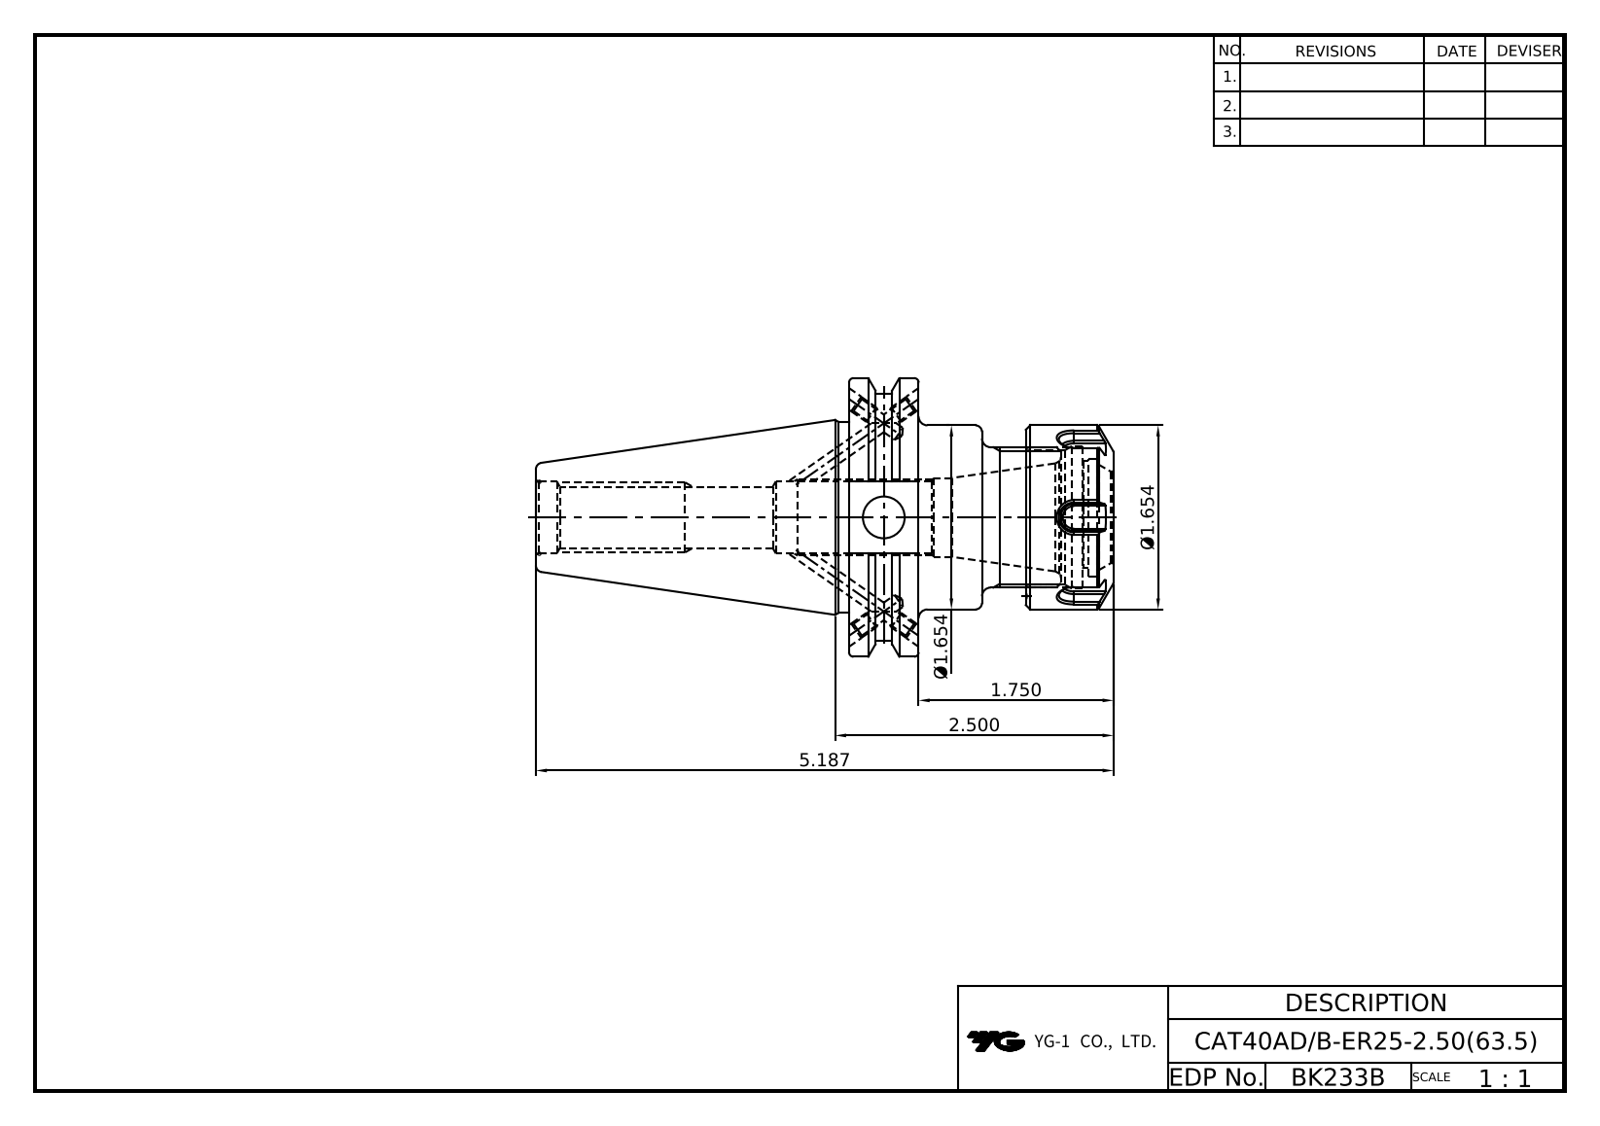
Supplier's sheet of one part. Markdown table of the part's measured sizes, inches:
| quantity | value |
| --- | --- |
| part name | LO-CAT40ADB-ER25-2.50; ER25NUT |
| STEP written by | Autodesk Inventor 2024 (AUTOMOTIVE_DESIGN) |
| units | inches |
| bodies | 2 solids, 164 faces (69 planar, 44 cylindrical, 51 other) |
| overall size | 5.187 × 2.5 × 2.405 |
| volume | 8.223 in³ |
| surface area | 51.17 in² |
| round holes (diameter × count) | 0.128 × 4, 0.157 × 4, 0.375 × 1, 0.527 × 1, 0.62 × 1, 0.642 × 1, 0.709 × 1, 0.823 × 1, 0.906 × 1, 1.055 × 1, 1.201 × 1, 1.28 × 1 |
| round bosses / shafts (diameter × count) | 2.5 × 1, 2.217 × 1, 1.717 × 1, 1.654 × 1, 1.26 × 1 |
| partial cylindrical surfaces (radius × count) | 0.02 × 12 |
| main face-to-face distances | 0.625, 1.588, 0.963, 2.096, 1.47, 0.508, 2.375, 1.75, 0.787, 0.28 |
| hole center spacings | 1.383, 0.019 |
